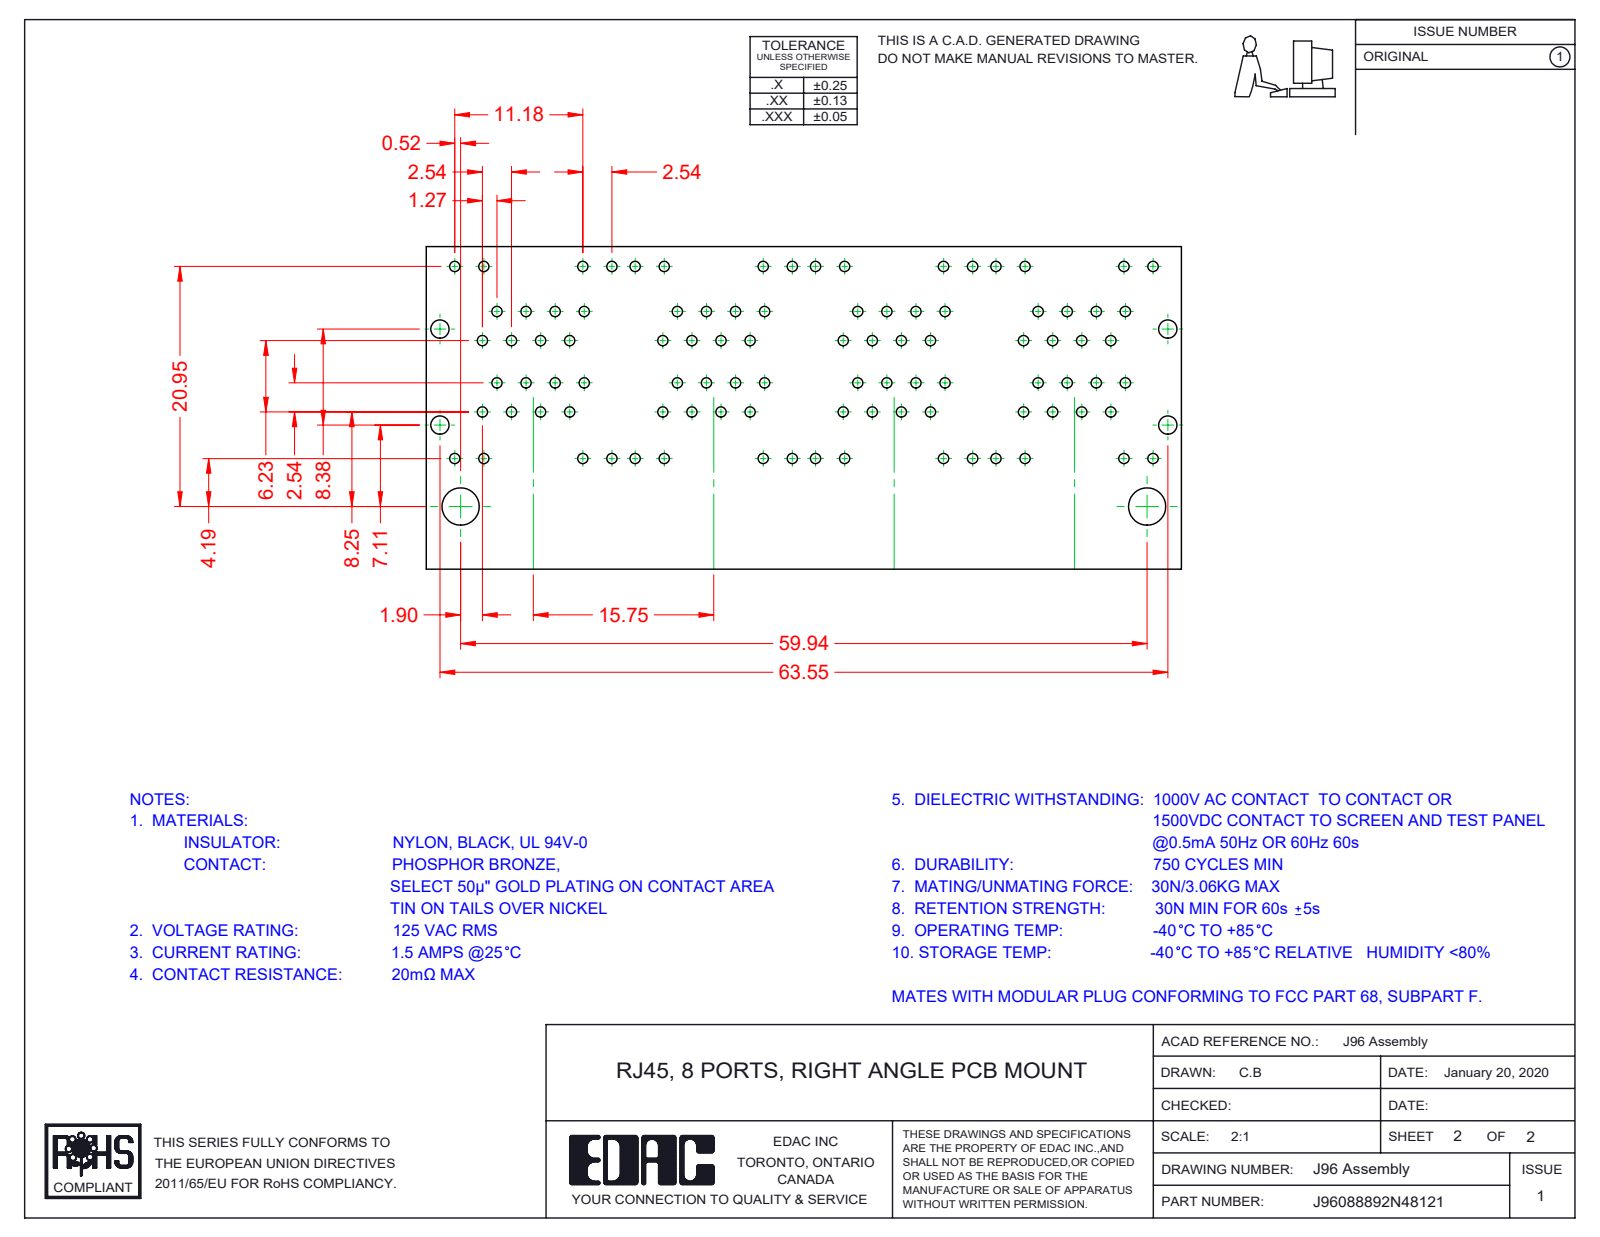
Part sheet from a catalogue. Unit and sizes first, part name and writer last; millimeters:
Units: millimetres
Overall size (bounding box): 64.05 × 29.58 × 28.68
Round holes (diameter × count): ⌀1.7 ×3
Round bosses / shafts (diameter × count): ⌀1.68 ×3
Partial cylindrical surfaces — rounded edges, fillets, slot ends (radius × count): R0.25 ×124, R0.35 ×73, R1 ×72, R0.5 ×49, R0.91 ×32, R0.2 ×21, R0.7 ×11, R0.22 ×8
Main face-to-face distances: 15.75, 0.35, 9.95, 1.17, 1.6, 0.54, 9.98, 10.18, 12.67, 3.37
Hole centre spacings: 15.75, 31.5
Volume: 24 160 mm³ · Surface area: 63 658 mm²
Bodies: 96 solids, 7658 faces (6069 planar, 1323 cylindrical, 266 other)
Part name (STEP PRODUCT): 96 Grounding_8 Ports; 96 Contact Lock Lower; 96 Shield_8 Ports LED - No EMI; 96 Contacts Lower (+8 more)
STEP written by: SolidWorks 2016 (CONFIG_CONTROL_DESIGN)
